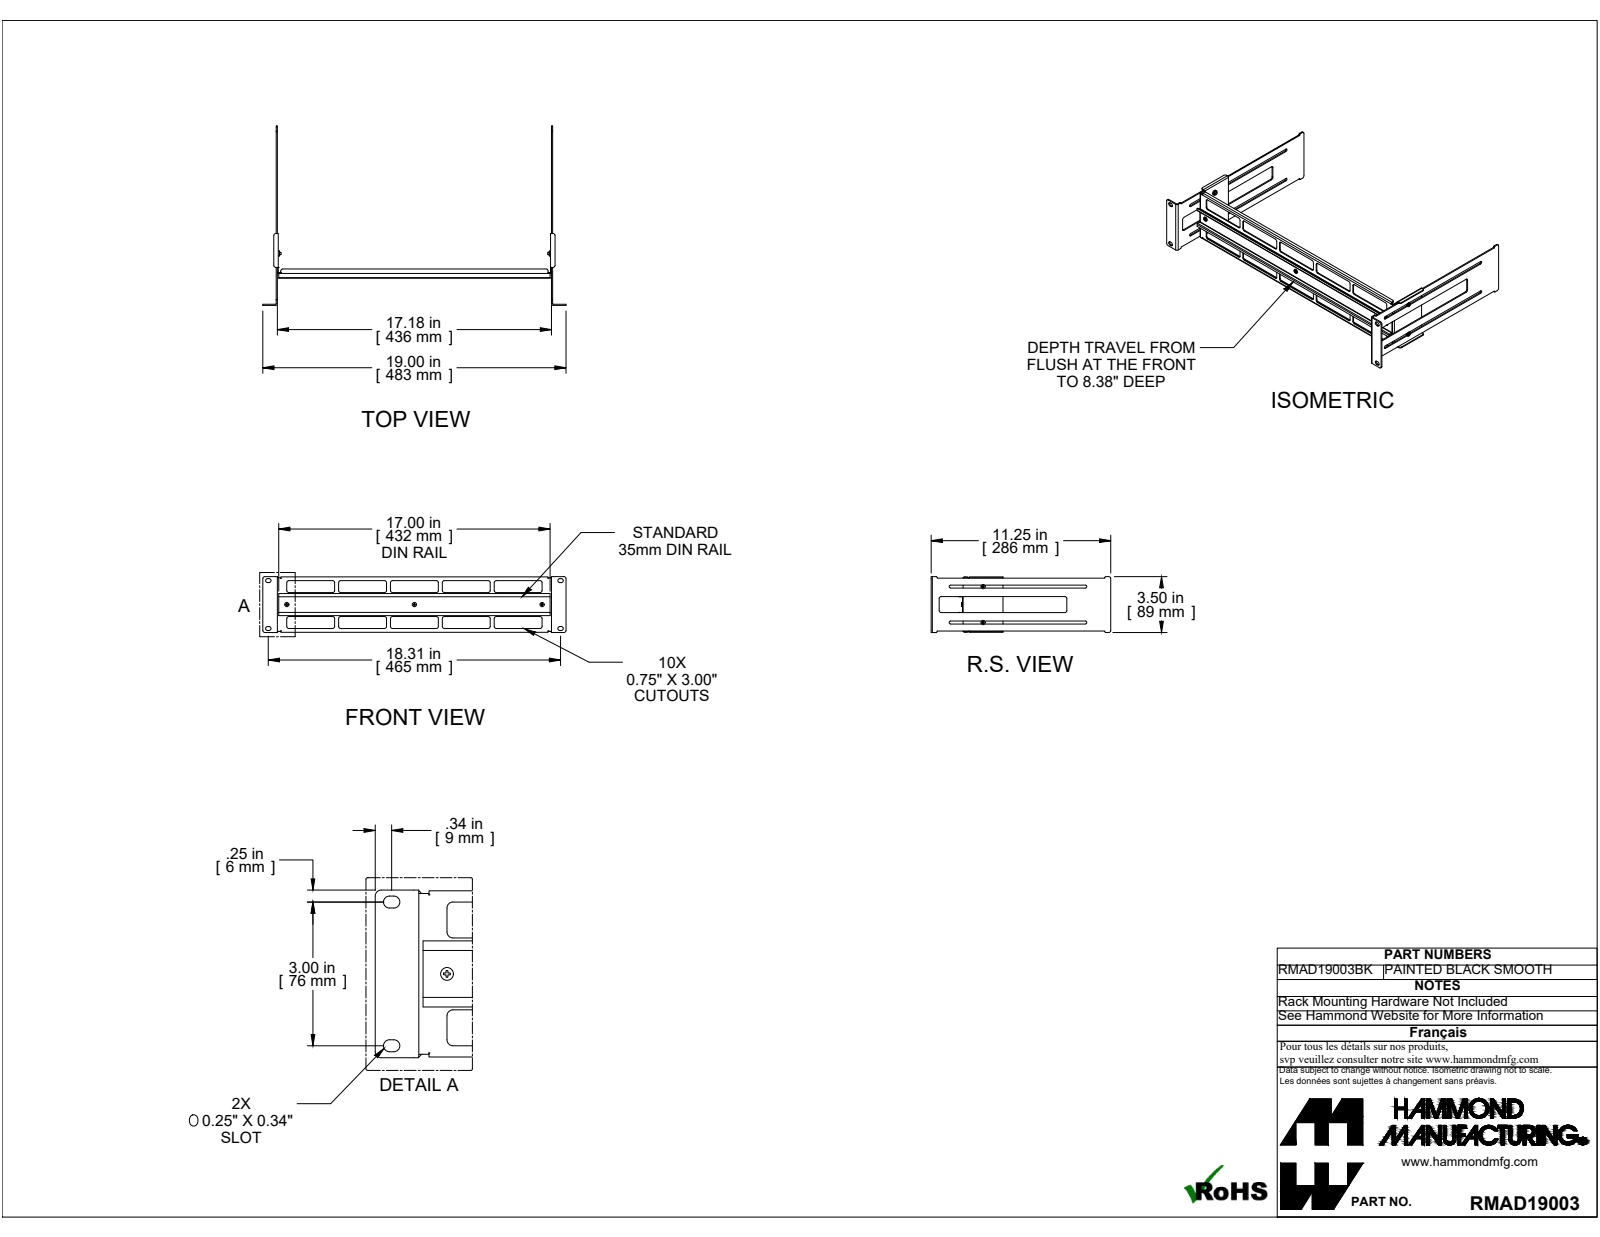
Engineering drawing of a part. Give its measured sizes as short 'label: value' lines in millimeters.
name: RMAD19003BK
written by: SolidWorks 2019 (AUTOMOTIVE_DESIGN)
unit: mm
bodies: 18 solids, 518 faces (297 planar, 172 cylindrical, 49 other)
size: 482.5 × 285.8 × 88.9
volume: 146 100 mm³; area: 211 200 mm²
holes: 5× ⌀3.3, 5× ⌀5.4, 3× ⌀4.8
bosses: 7× ⌀6.8, 7× ⌀3.5, 5× ⌀7.9, 5× ⌀6.6, 5× ⌀5.4
rounds: 70× R3.2, 8× R0.7, 8× R2.2, 8× R2.4, 4× R0.5, 4× R1.4, 4× R1.5, 2× R0.9
face distances: 1.4, 1.8, 438.1, 436.3, 0.9, 440, 2.4, 3.3, 436.7, 434.8
hole spacings: 203.2, 57.2, 406.4
